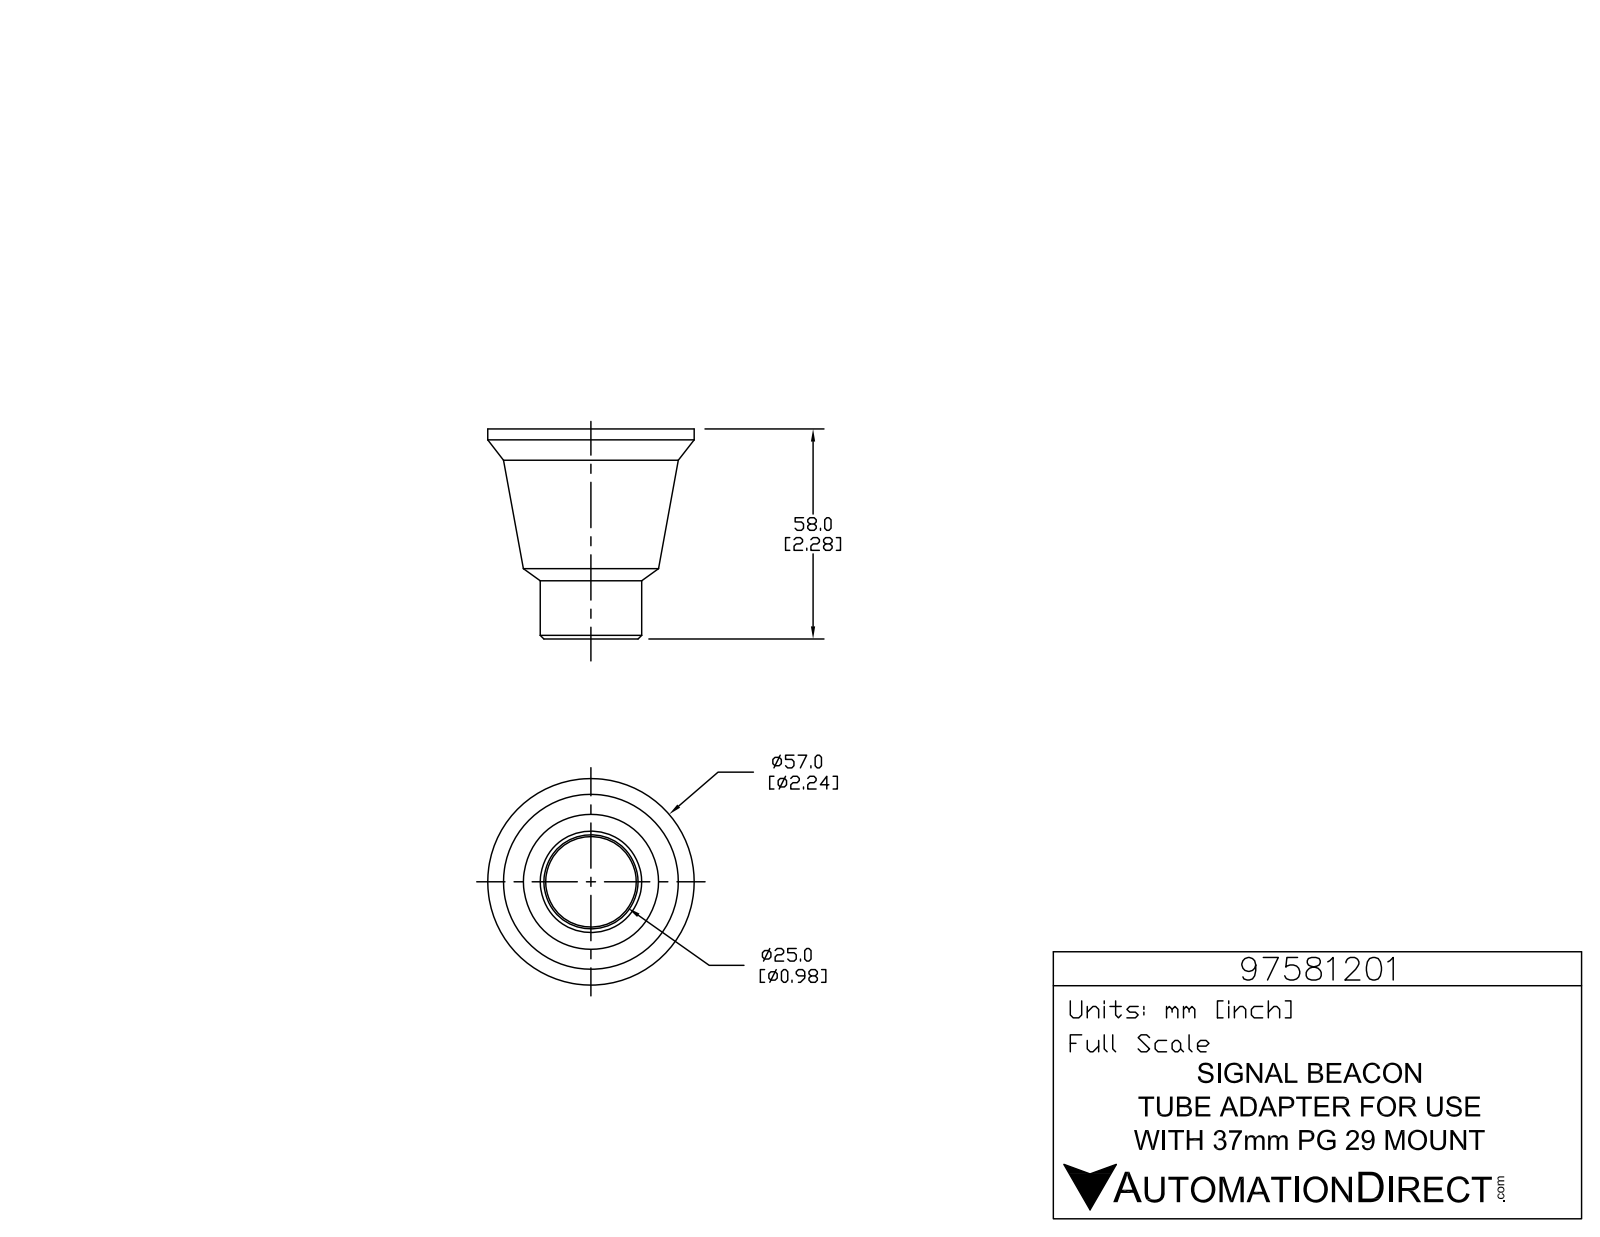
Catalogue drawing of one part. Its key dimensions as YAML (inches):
part_name: "97581201"
step_written_by: "SolidWorks 2017 (AUTOMOTIVE_DESIGN)"
units: inches
bodies: {solids: 1, faces: 757, planar: 80, cylindrical: 10, other: 667}
overall_size: [2.26, 2.236, 2.236]
volume: 0.762
surface_area: 23.69
round_holes:
  - {diameter: 0.709, count: 1}
  - {diameter: 0.992, count: 1}
  - {diameter: 1.496, count: 1}
  - {diameter: 2.069, count: 1}
round_bosses_or_shafts:
  - {diameter: 2.236, count: 1}
face_to_face_distances: [1.543, 0.059, 1.602, 0.657, 0.717, 2.26, 1.537, 0.88, 0.82, 0.723]
